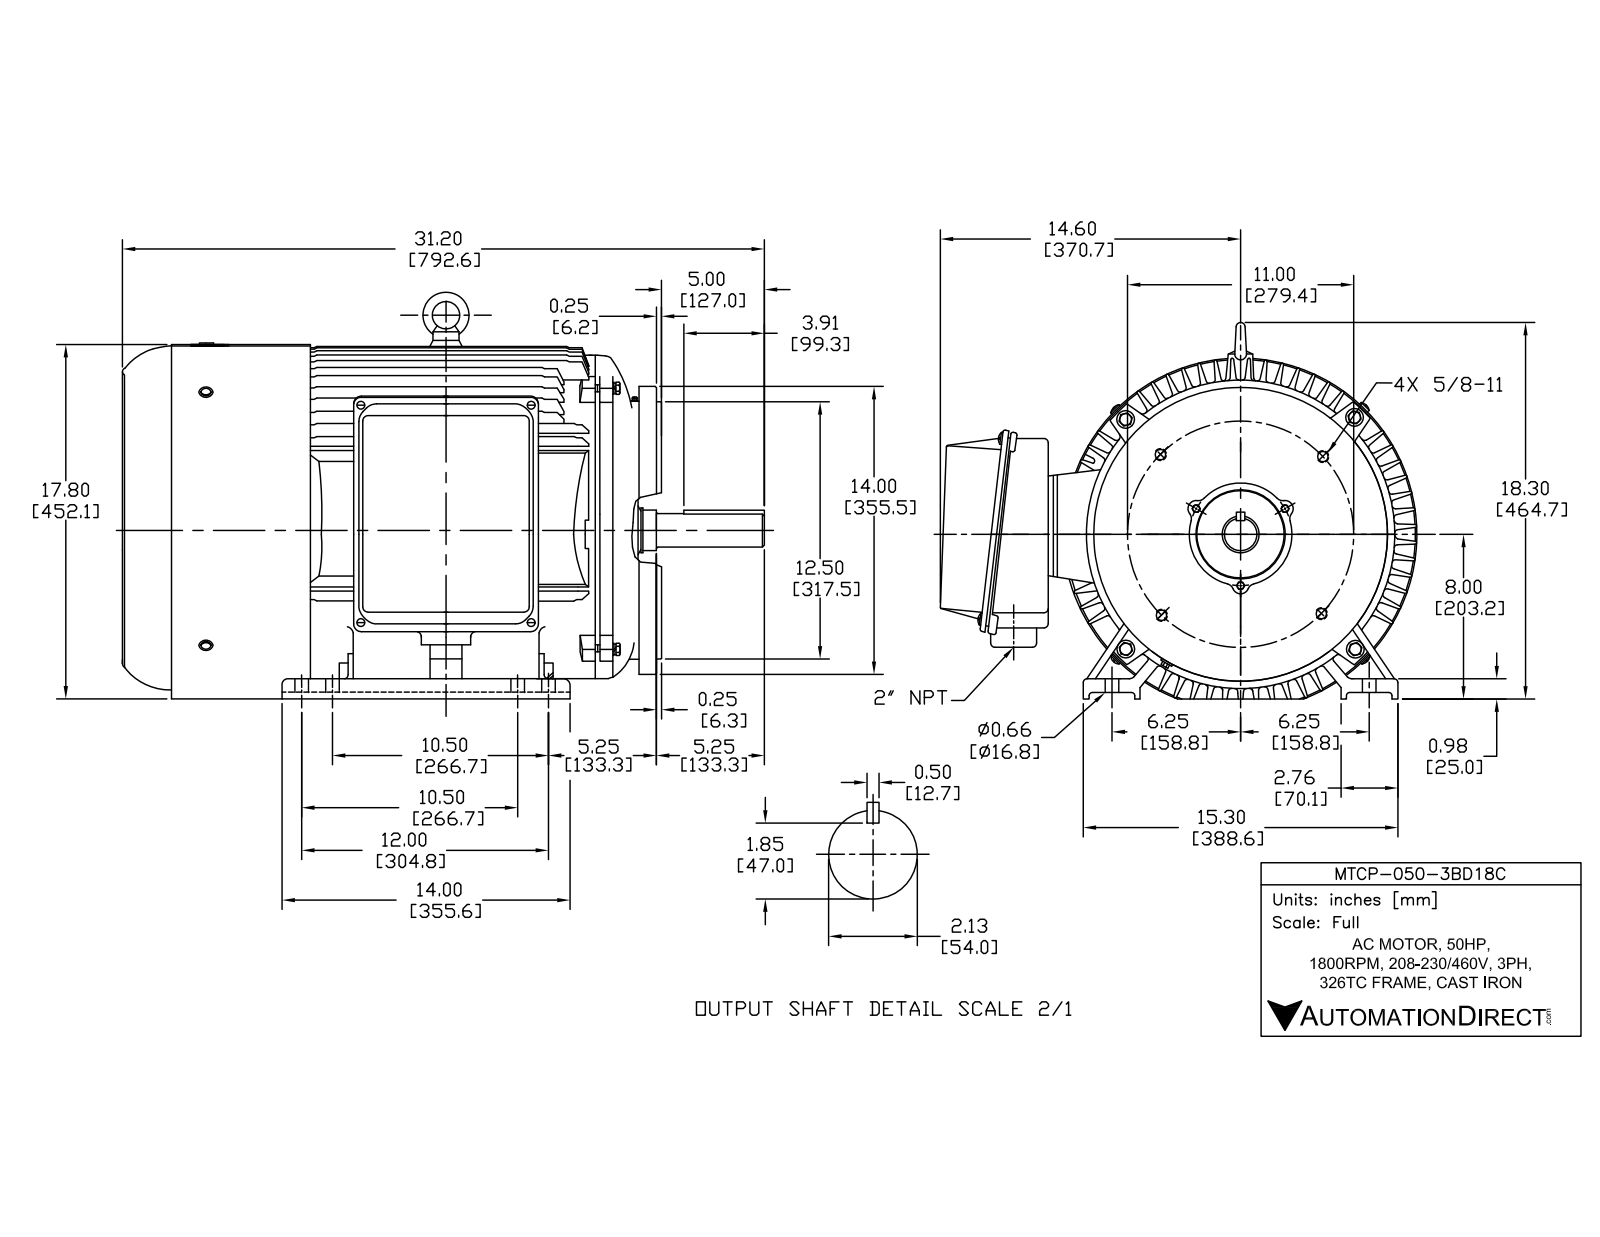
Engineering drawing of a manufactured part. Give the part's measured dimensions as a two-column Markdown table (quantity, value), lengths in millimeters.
| quantity | value |
| --- | --- |
| part name | hexagon head bolts-full thread gb_GB_FASTENER_BOLT_STBAB A M8X60-N; hexagon head bolts-full thread gb_GB_FASTENER_BOLT_STBAB A M6X12-N; hexagon head bolts-full thread gb_GB_FASTENER_BOLT_STBAB A M12X50-N; hexagon head bolts-full thread gb_GB_FASTENER_BOLT_STBAB A M8X20-N (+8 more) |
| STEP written by | SolidWorks 2017 (AUTOMOTIVE_DESIGN) |
| units | millimeters |
| bodies | 58 solids, 4159 faces (1148 planar, 1428 cylindrical, 1583 other) |
| overall size | 780.85 × 584.3 × 517.4 |
| volume | 17 500 000 mm³ |
| surface area | 4 095 000 mm² |
| round holes (diameter × count) | 10 × 21, 6.8 × 8, 17 × 8, 5 × 4, 6.4 × 4, 6.68 × 4, 9 × 4, 10.2 × 4, 11.39 × 4, 12.9 × 4, 13 × 4, 13.49 × 4 |
| round bosses / shafts (diameter × count) | 8 × 11, 12 × 8, 24 × 4, 19.1 × 4, 9.88 × 4, 6 × 4, 10 × 2, 445 × 1 |
| partial cylindrical surfaces (radius × count) | 1 × 223, 5 × 104, 3 × 82, 2 × 76, 0.5 × 48, 1.5 × 35, 10 × 27, 8 × 24 |
| main face-to-face distances | 6, 1.5, 123.91, 5, 654.1, 652.6, 25, 24.5, 629.6, 628.1 |
| hole center spacings | 100, 208, 75, 249.73, 38.1, 67.3, 70, 101.6 |
